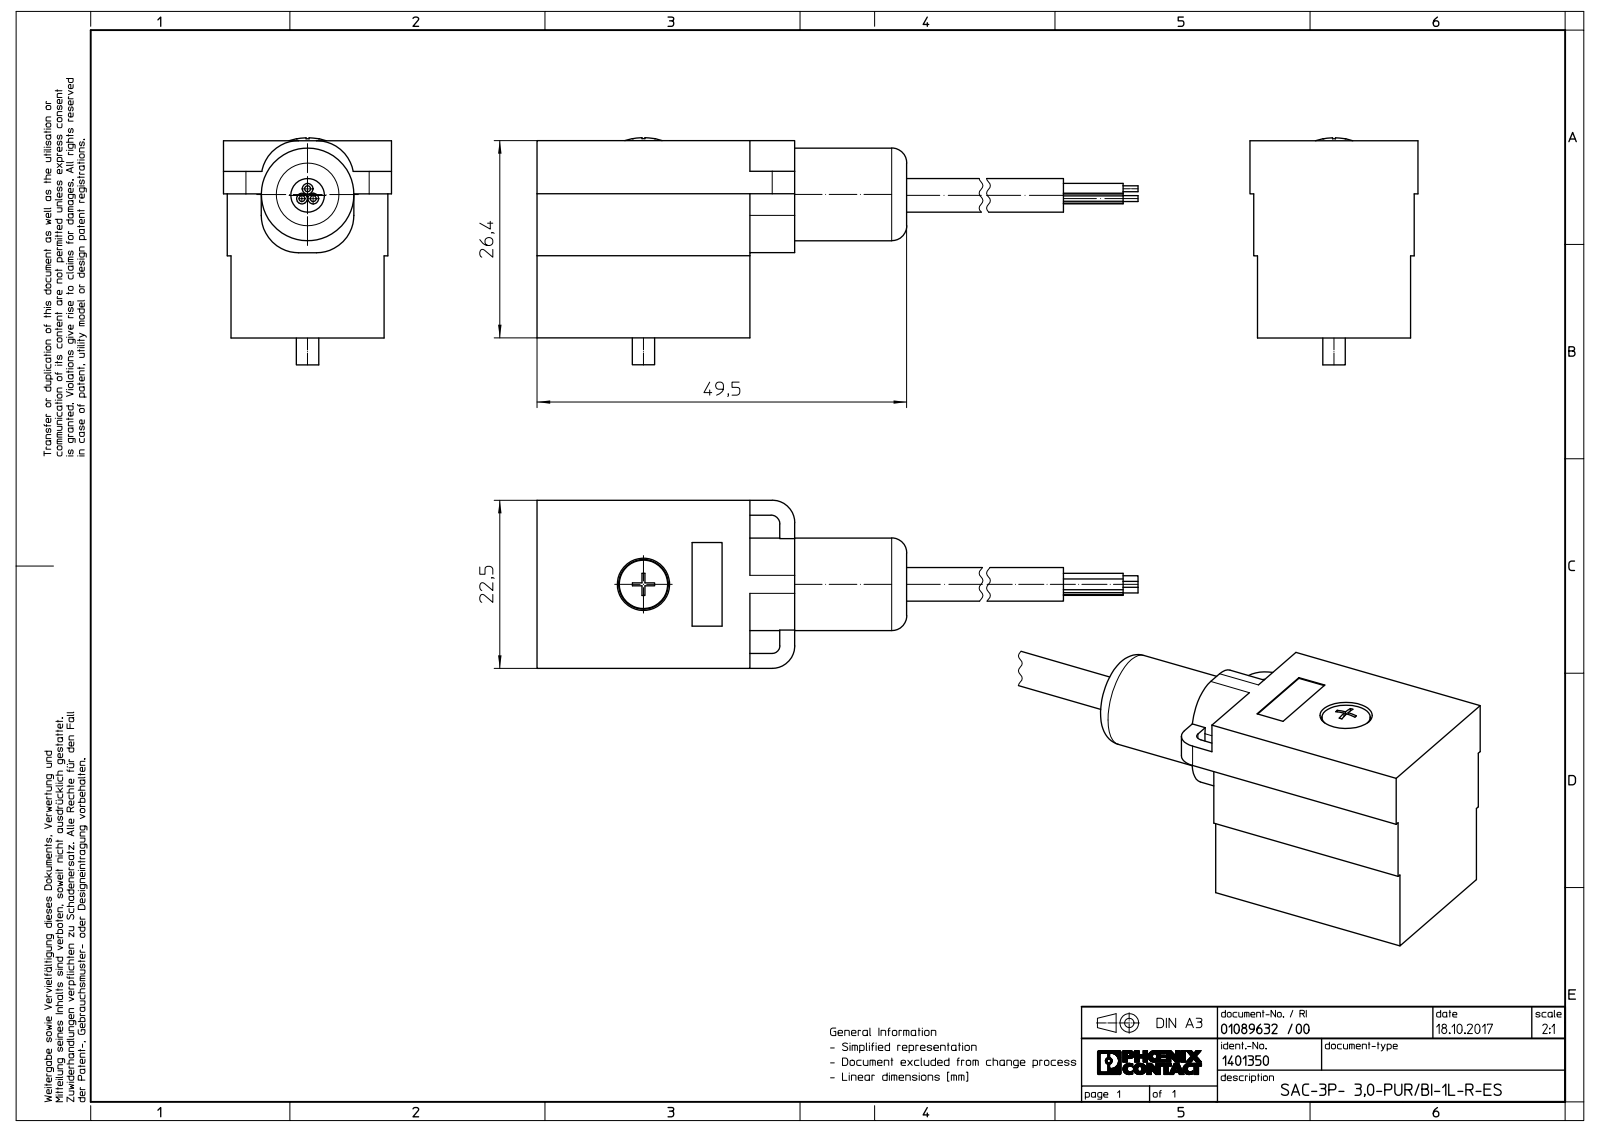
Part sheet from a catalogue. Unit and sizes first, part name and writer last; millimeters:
Units: millimetres
Overall size (bounding box): 159.5 × 30.39 × 22.5
Round holes (diameter × count): ⌀6.1 ×1, ⌀7 ×1
Round bosses / shafts (diameter × count): ⌀0.8 ×3, ⌀1.43 ×2, ⌀12.4 ×1, ⌀4.5 ×1, ⌀3 ×1
Partial cylindrical surfaces — rounded edges, fillets, slot ends (radius × count): R5 ×4, R3 ×2, R0.71 ×1, R1 ×1, R1.16 ×1
Main face-to-face distances: 0.5, 21.5, 21, 1, 22, 28.5, 24.9, 20.5, 22.5, 1.5
Volume: 19 763 mm³ · Surface area: 6 966 mm²
Bodies: 1 solid, 132 faces (93 planar, 33 cylindrical, 6 other)
Part name (STEP PRODUCT): 5812-1 Actuator cable - SAC-3P- 3,0-PURBI-1L-R-ES - 1401350; 5812 Actuator cable - SAC-3P- 3,0-PURBI-1L-R-ES - 1401350
STEP written by: Alibre (AUTOMOTIVE_DESIGN)
